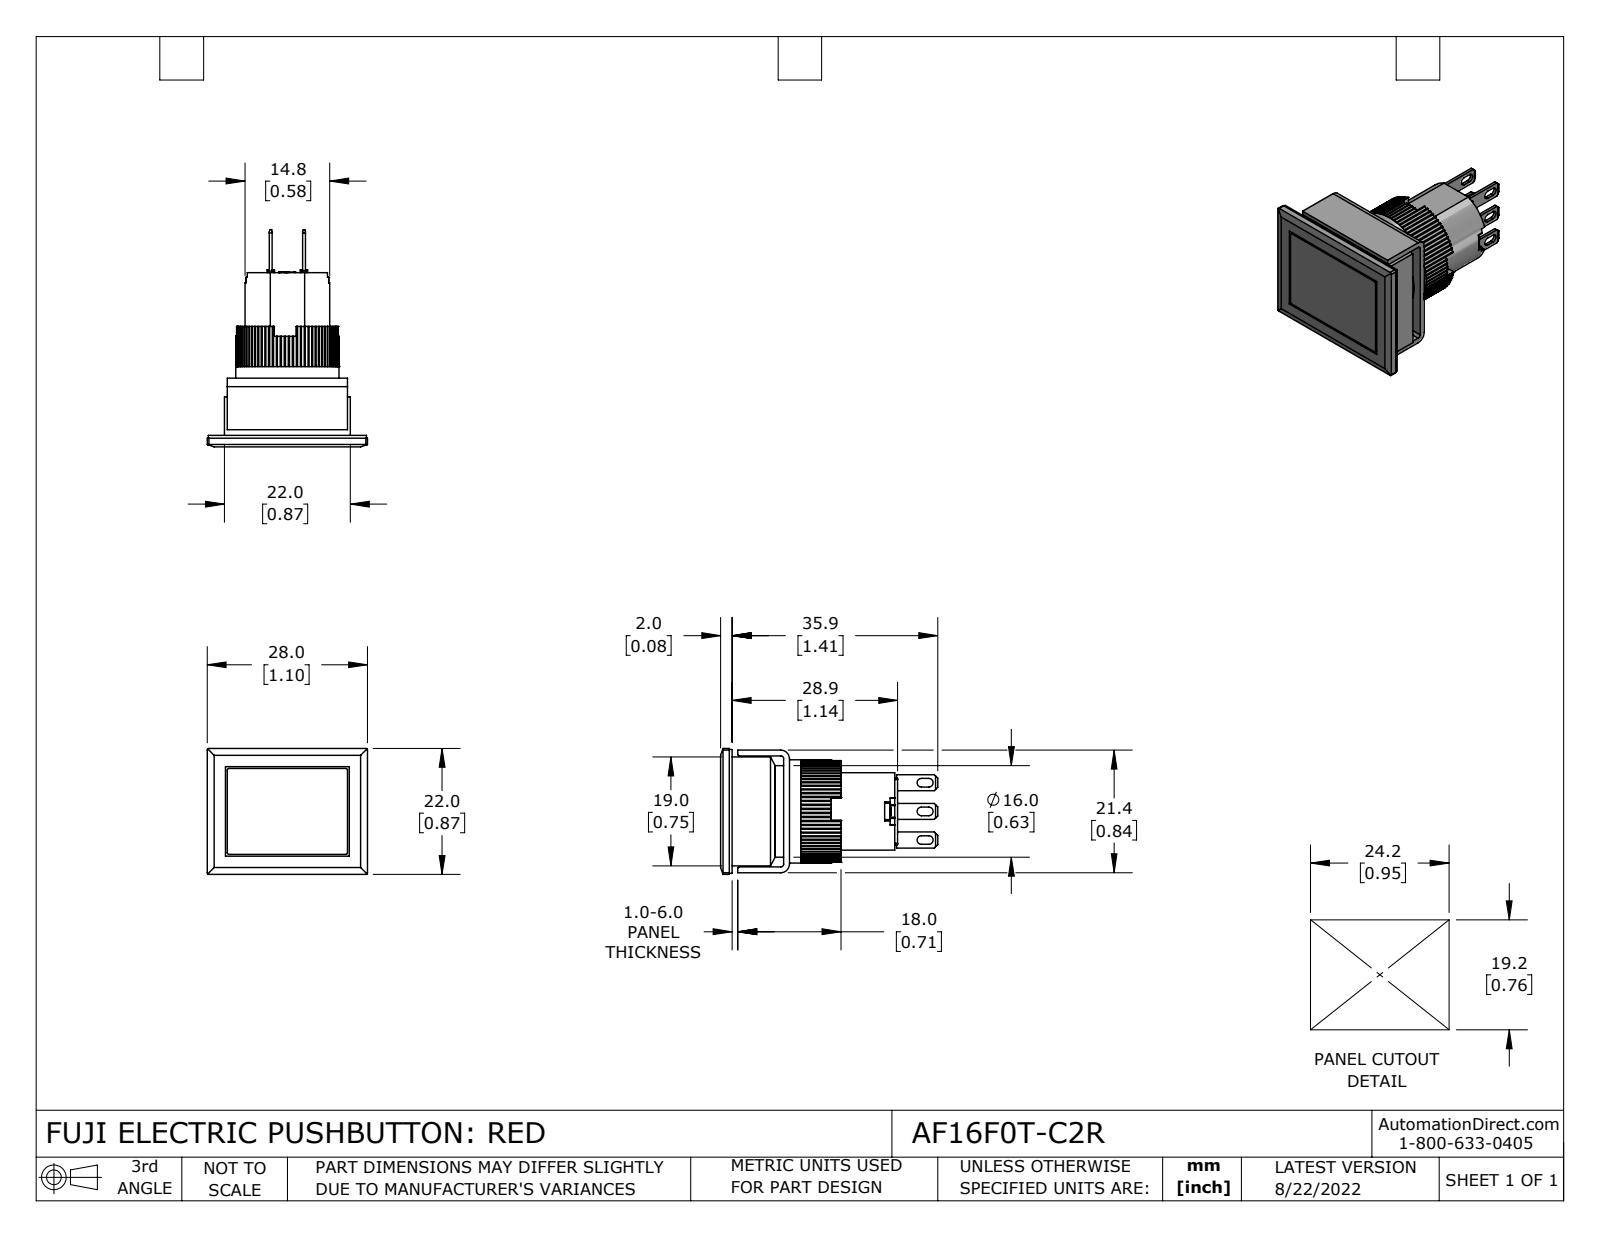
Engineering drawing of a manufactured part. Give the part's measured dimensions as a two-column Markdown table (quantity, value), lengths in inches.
| quantity | value |
| --- | --- |
| part name | AF16F0T-C2R |
| STEP written by | SolidWorks 2021 (CONFIG_CONTROL_DESIGN) |
| units | inches |
| bodies | 12 solids, 798 faces (620 planar, 176 cylindrical, 2 other) |
| overall size | 1.492 × 1.102 × 0.866 |
| volume | 0.541 in³ |
| surface area | 11.85 in² |
| round holes (diameter × count) | 0.039 × 1, 0.709 × 1 |
| round bosses / shafts (diameter × count) | 0.63 × 1, 0.583 × 1 |
| partial cylindrical surfaces (radius × count) | 0.01 × 80, 0.008 × 12, 0.012 × 8, 0.03 × 6, 0.02 × 2, 0.059 × 2 |
| main face-to-face distances | 0.374, 0.059, 0.02, 0.142, 0.039, 0.315, 0.232, 0.083, 0.079, 0.756 |
